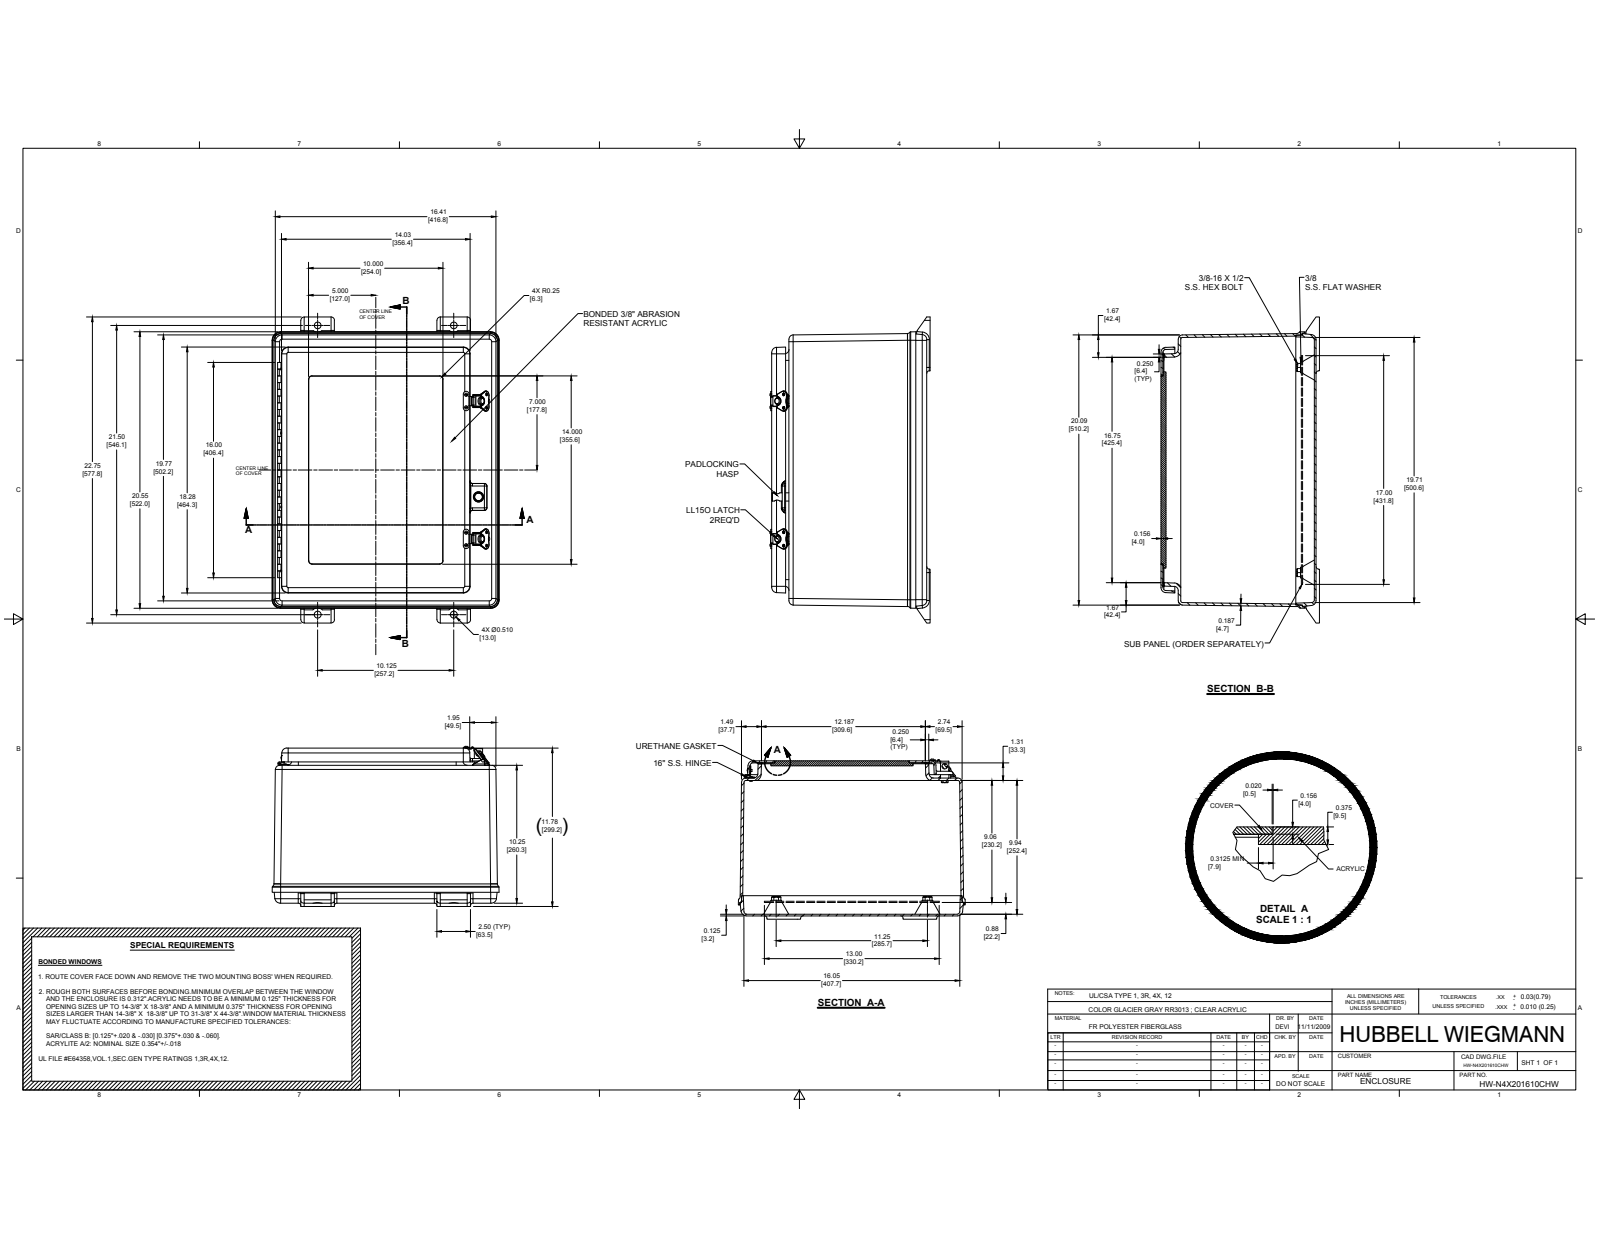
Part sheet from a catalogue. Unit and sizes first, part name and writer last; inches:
Units: inches
Overall size (bounding box): 22.75 × 16.875 × 11.909
Round holes (diameter × count): ⌀0.13 ×20, ⌀0.063 ×8, ⌀0.065 ×8, ⌀0.138 ×4, ⌀0.187 ×4, ⌀0.307 ×4, ⌀0.563 ×4, ⌀0.5 ×2, ⌀0.51 ×2, ⌀0.125 ×1, ⌀0.135 ×1, ⌀0.156 ×1
Round bosses / shafts (diameter × count): ⌀0.297 ×8, ⌀0.14 ×8, ⌀0.5 ×2, ⌀0.563 ×1, ⌀0.25 ×1, ⌀0.201 ×1, ⌀0.2 ×1
Partial cylindrical surfaces — rounded edges, fillets, slot ends (radius × count): R0.01 ×59, R0.25 ×28, R0.187 ×25, R0.5 ×12, R0.313 ×10, R0.375 ×10, R0.03 ×8, R0.23 ×8
Main face-to-face distances: 0.187, 0.125, 11.409, 11.535, 0.375, 11.159, 11.034, 0.156, 11.378, 11.253
Hole centre spacings: 10.25, 4.75, 1.526, 3.176, 10.25, 11.135, 13.619, 13.781
Volume: 320.5 in³ · Surface area: 3 457 in²
Bodies: 41 solids, 1166 faces (453 planar, 444 cylindrical, 269 other)
Part name (STEP PRODUCT): WPN201610SHWT; WPN2016B; SS HINGE COVER (16); 0.13 RIVET PIN (+7 more)
STEP written by: Autodesk Inventor 2014 (AUTOMOTIVE_DESIGN)
